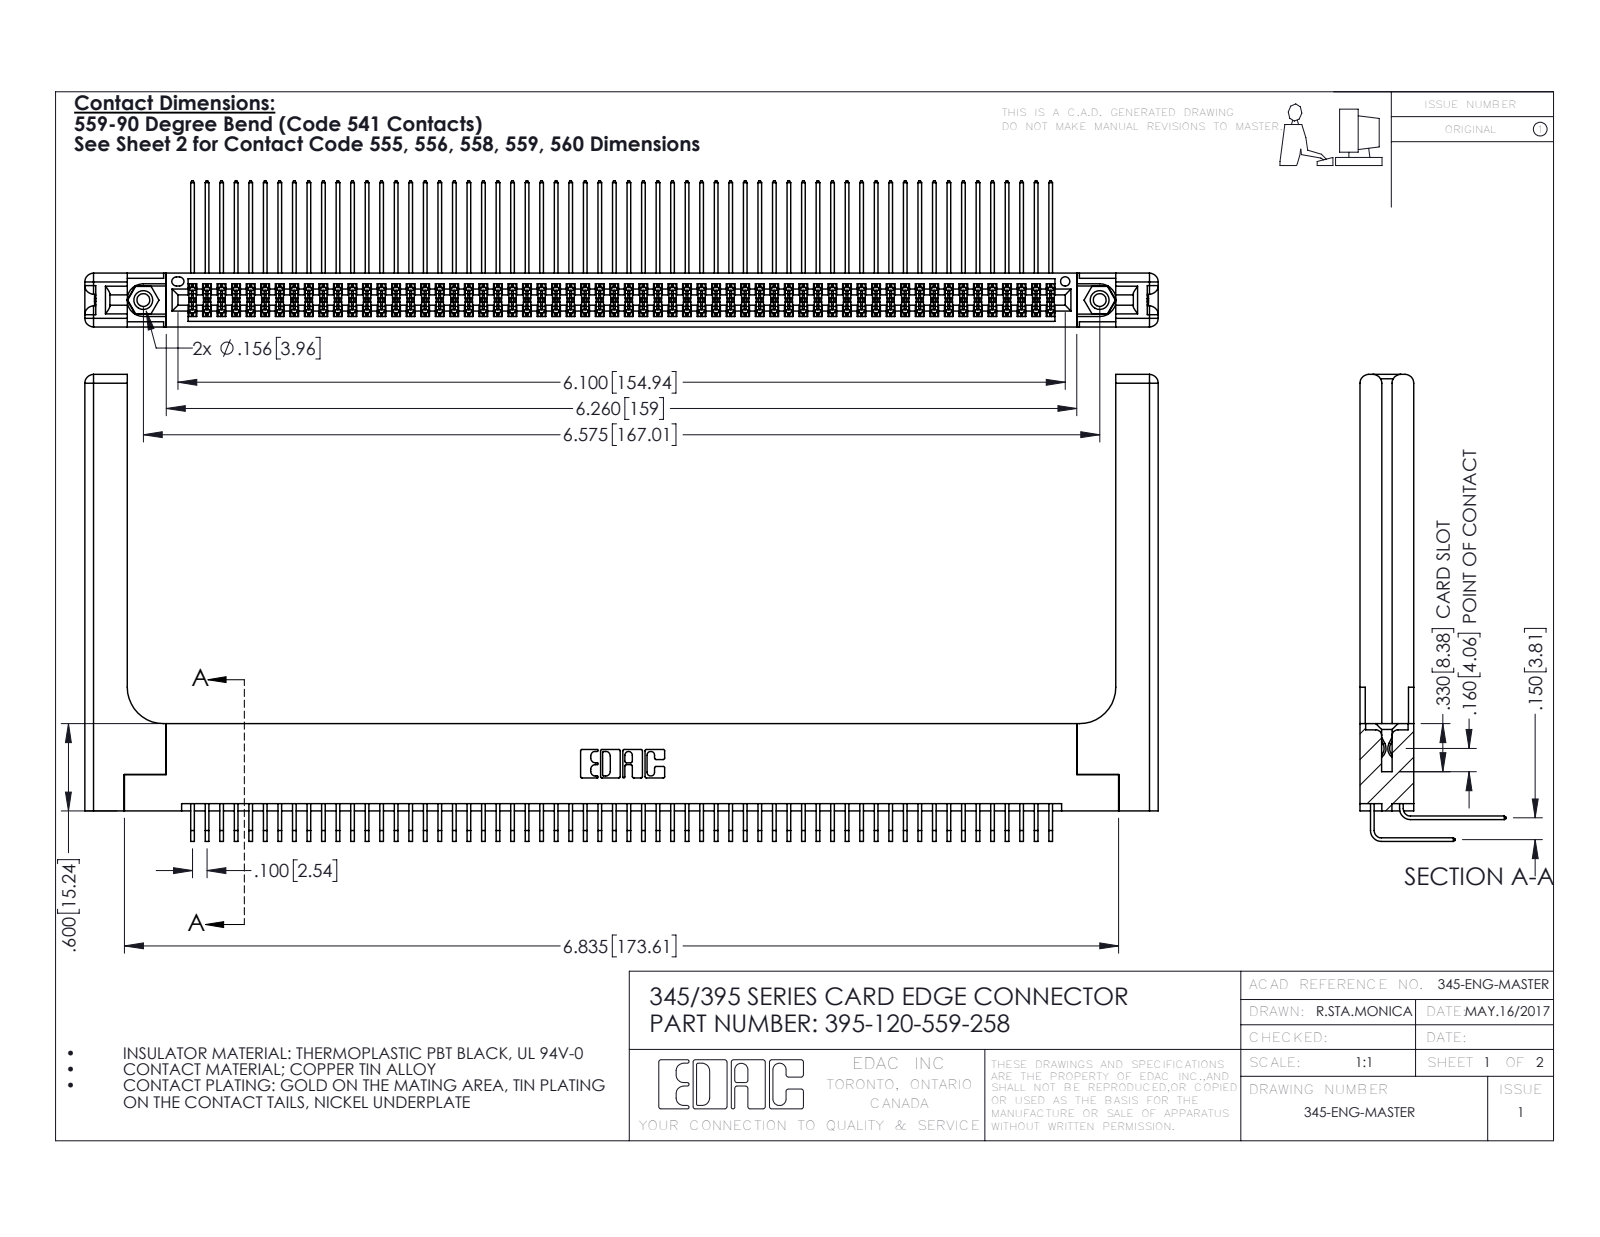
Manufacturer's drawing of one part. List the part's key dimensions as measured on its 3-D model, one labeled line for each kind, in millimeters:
Part name (STEP PRODUCT): 345-292-001_558 559 Tail - 1; 345 Part_Flush Mounting Lugs - 0.156 Dia-TH; 345-292-001_559 Tail - 2; 345-220-058_345-220-058 (+2 more)
STEP written by: SolidWorks 2016 (CONFIG_CONTROL_DESIGN)
Units: millimetres
Bodies: 125 solids, 6622 faces (4428 planar, 2134 cylindrical, 60 other)
Overall size (bounding box): 187.4 × 81.5 × 25.5
Volume: 27 550 mm³ · Surface area: 36 850 mm²
Round holes (diameter × count): ⌀2.3 ×2, ⌀3.2 ×2, ⌀4 ×2, ⌀1.6 ×1
Round bosses / shafts (diameter × count): ⌀3.9 ×2
Partial cylindrical surfaces — rounded edges, fillets, slot ends (radius × count): R0.2 ×181, R0.3 ×22, R1.5 ×16, R0.2 ×6, R0.8 ×6, R0.7 ×3, R0.4 ×2, R0.5 ×2
Main face-to-face distances: 1.8, 7.6, 9.4, 5.1, 2.5, 6.9, 0.6, 5.7, 4.4, 3.8
Hole centre spacings: 6.9, 161, 167
